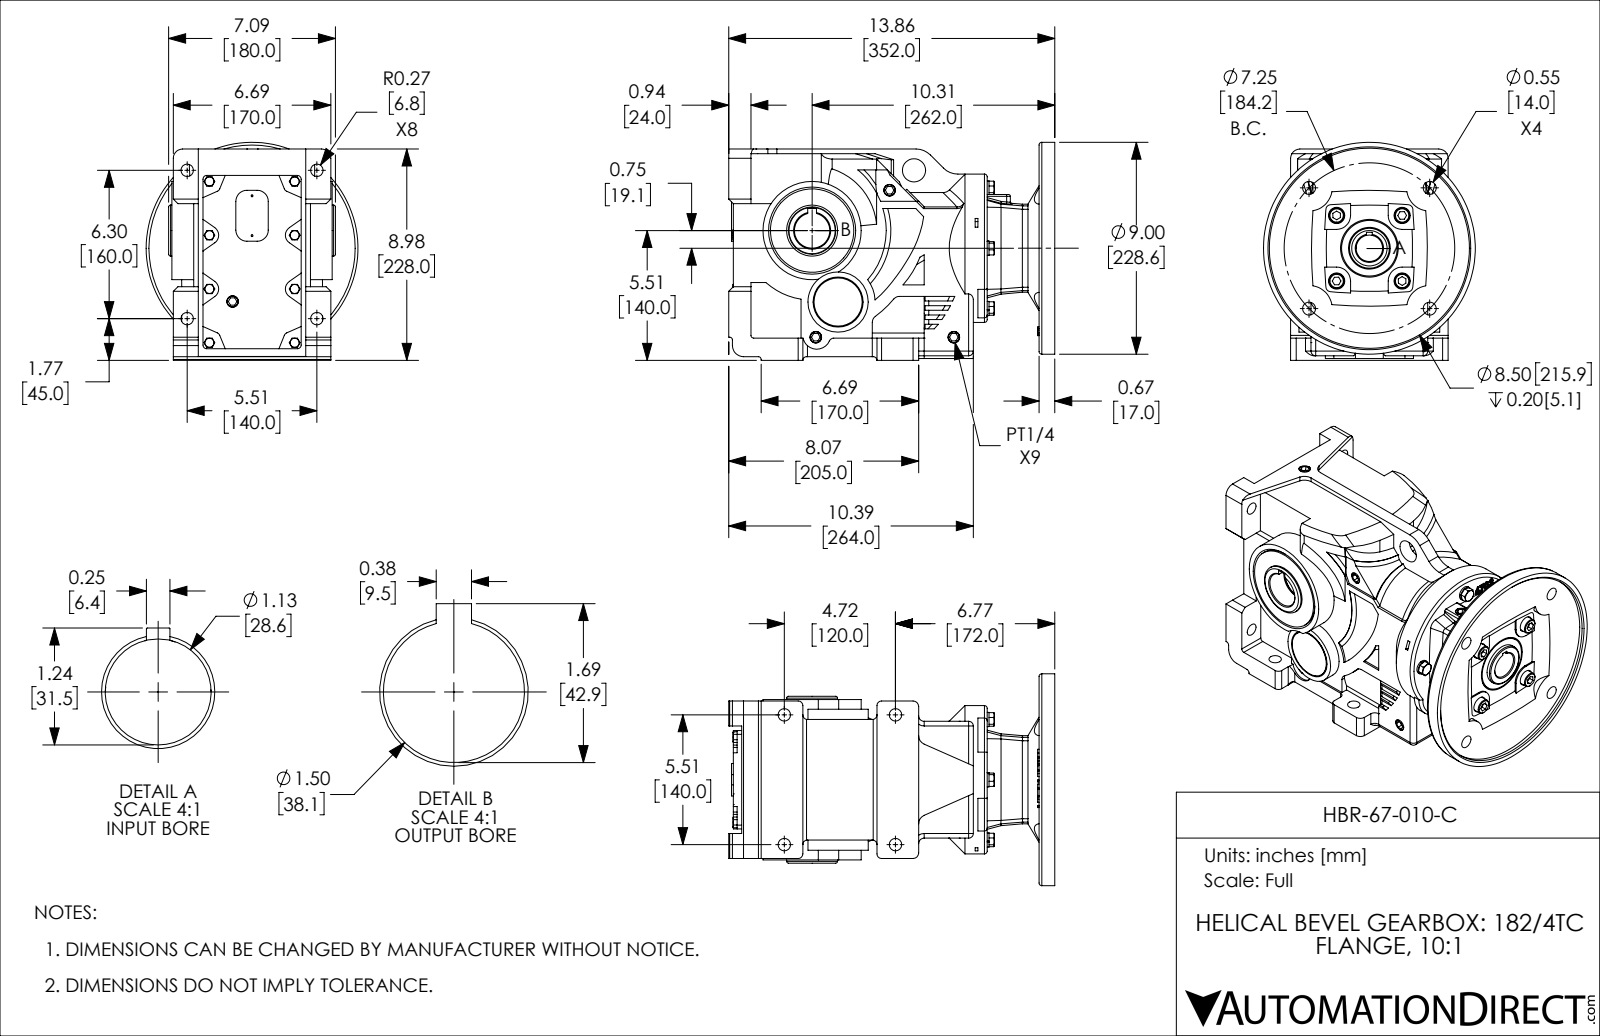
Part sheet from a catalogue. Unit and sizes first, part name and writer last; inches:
Units: inches
Overall size (bounding box): 13.858 × 9.262 × 9
Round holes (diameter × count): ⌀0.531 ×8, ⌀0.323 ×4, ⌀0.354 ×4, ⌀0.551 ×4, ⌀0.689 ×4, ⌀0.079 ×2, ⌀0.984 ×1, ⌀1.125 ×1, ⌀1.417 ×1, ⌀1.5 ×1, ⌀1.575 ×1, ⌀8.5 ×1
Round bosses / shafts (diameter × count): ⌀0.63 ×4, ⌀0.606 ×4, ⌀0.315 ×4, ⌀9 ×1, ⌀6.299 ×1, ⌀4.173 ×1, ⌀3.543 ×1, ⌀2.559 ×1
Partial cylindrical surfaces — rounded edges, fillets, slot ends (radius × count): R0.197 ×20, R0.157 ×12, R0.394 ×11, R0.079 ×7, R0.472 ×5, R0.591 ×5, R0.236 ×4, R0.689 ×4
Main face-to-face distances: 0.197, 0.079, 0.469, 0.945, 0.059, 13.461, 12.992, 8.78, 4.961, 0.118
Hole centre spacings: 2.563, 5.728, 1.656, 1.817, 2.559, 3.619, 4.125, 4.125
Volume: 513.2 in³ · Surface area: 714.3 in²
Bodies: 1 solid, 1100 faces (560 planar, 258 cylindrical, 282 other)
Part name (STEP PRODUCT): HBR-67-010-C
STEP written by: SolidWorks 2018 (AUTOMOTIVE_DESIGN)
